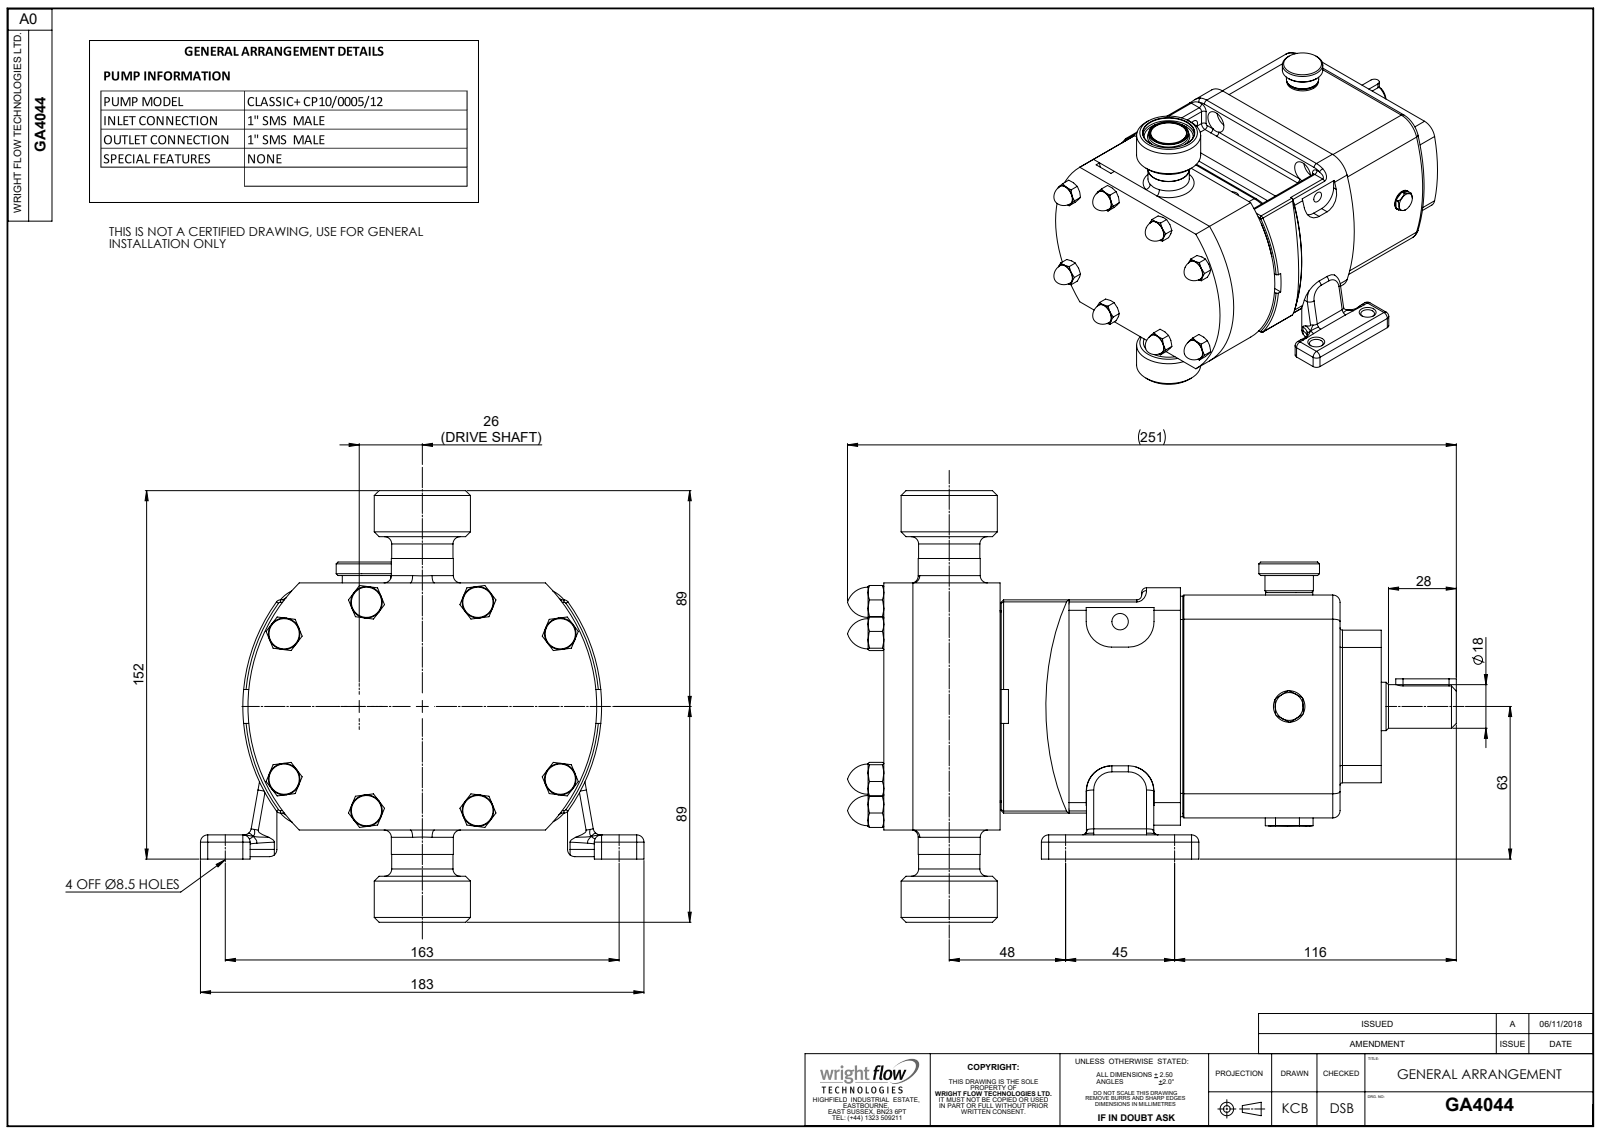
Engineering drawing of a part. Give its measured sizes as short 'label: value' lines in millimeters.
name: Copy of Z94-5101-11 - 1 INCH SMS681^GA4044; GA4044; Copy of CP10-0005-12 V L^GA4044
written by: SolidWorks 2023 (AUTOMOTIVE_DESIGN)
unit: mm
bodies: 3 solids, 797 faces (252 planar, 224 cylindrical, 321 other)
size: 251.35 × 183.1 × 178.15
volume: 2 273 000 mm³; area: 176 862 mm²
holes: 4× ⌀8.5, 4× ⌀14, 2× ⌀7.63, 1× ⌀6.8, 1× ⌀22.2, 1× ⌀22.53, 1× ⌀32
bosses: 2× ⌀30, 1× ⌀39.7, 1× ⌀25.6, 1× ⌀25.3, 1× ⌀25.02, 1× ⌀24.6, 1× ⌀19.99, 1× ⌀19.98
rounds: 32× R2, 32× R3, 12× R13.5, 6× R3.5, 6× R10.5, 4× R5.5, 4× R6, 4× R9
face distances: 5, 97, 205.35, 92, 2, 16, 102, 17, 124, 81.35
hole spacings: 45, 76, 77.01, 108.2, 162.6, 168.71, 51.22, 75.07
